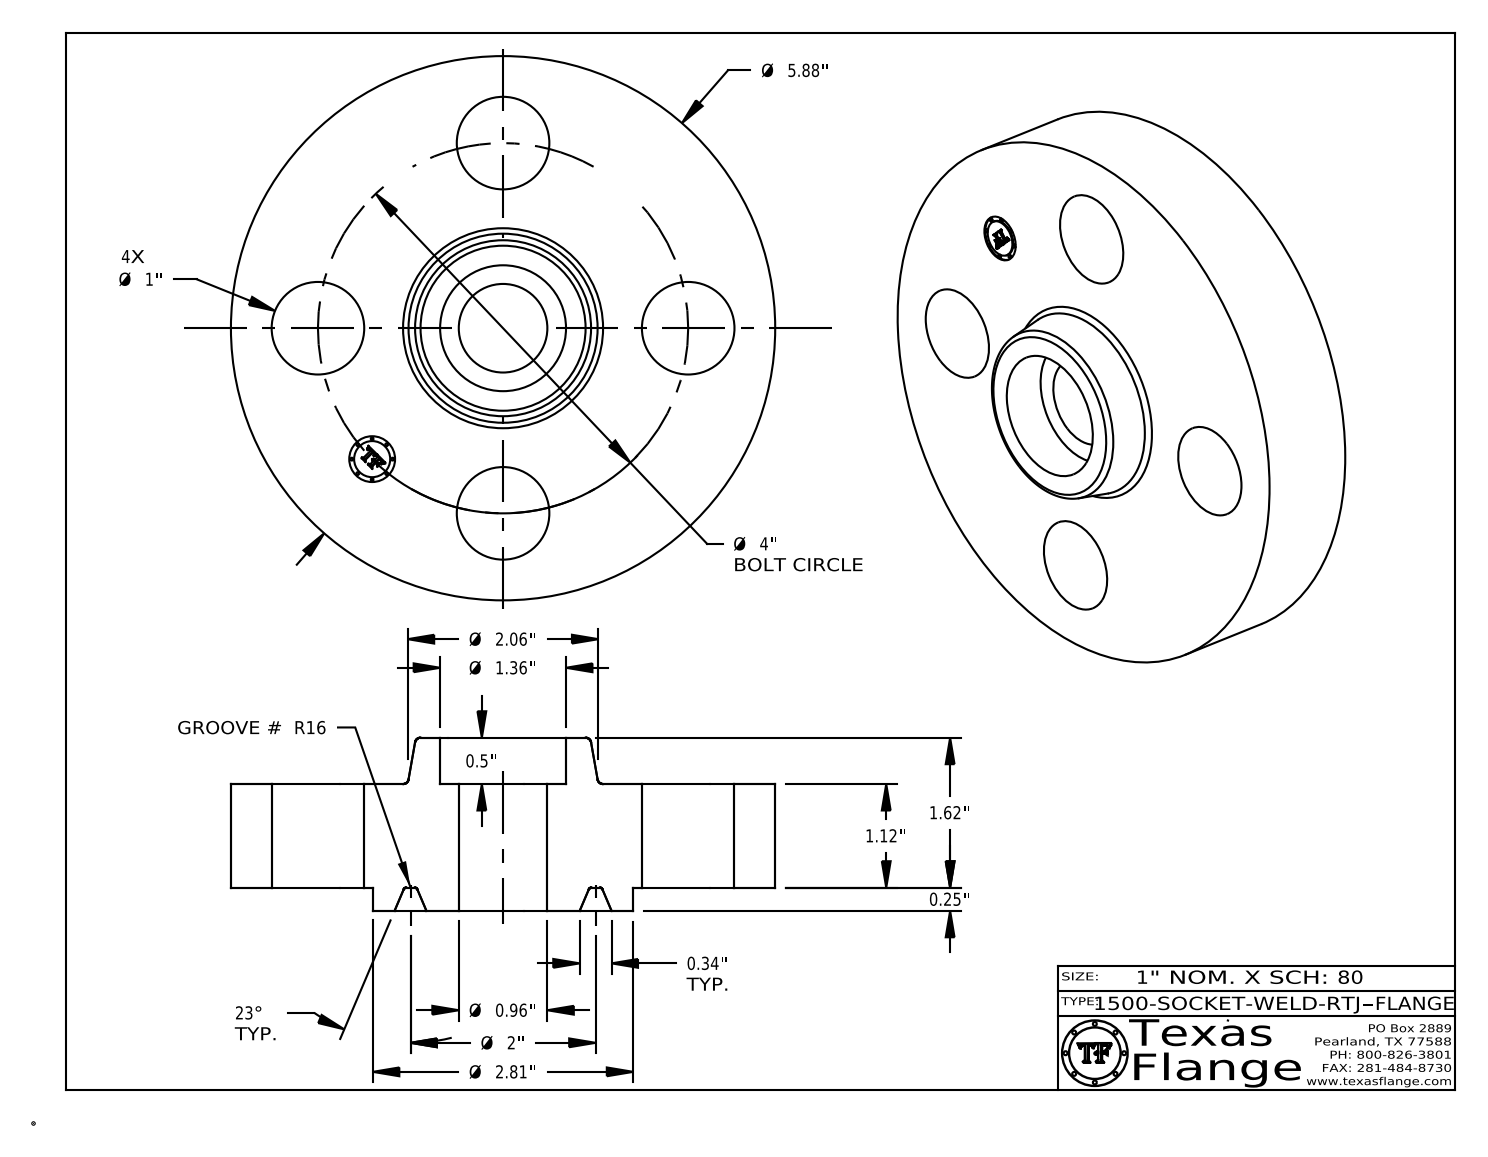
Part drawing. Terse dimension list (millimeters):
name: 1500-SOCKET-WELD-RTJ
written by: CATIA V5 STEP AP214 (AUTOMOTIVE_DESIGN)
unit: mm
bodies: 1 solid, 422 faces (372 planar, 36 cylindrical, 14 other)
size: 149.4 × 149.4 × 47.5
volume: 457 000 mm³; area: 60 850 mm²
holes: 4× ⌀25.4, 1× ⌀12.6, 1× ⌀24.3, 1× ⌀34.5
bosses: 8× ⌀0.8, 1× ⌀149.4, 1× ⌀71.5, 1× ⌀9.9
face distances: 28.4, 6.4, 34.8, 47.5, 41.1, 12.7, 0.4, 34.4, 28.1, 13.1
hole spacings: 50.8, 71.8, 38.9, 93.9, 101.6
